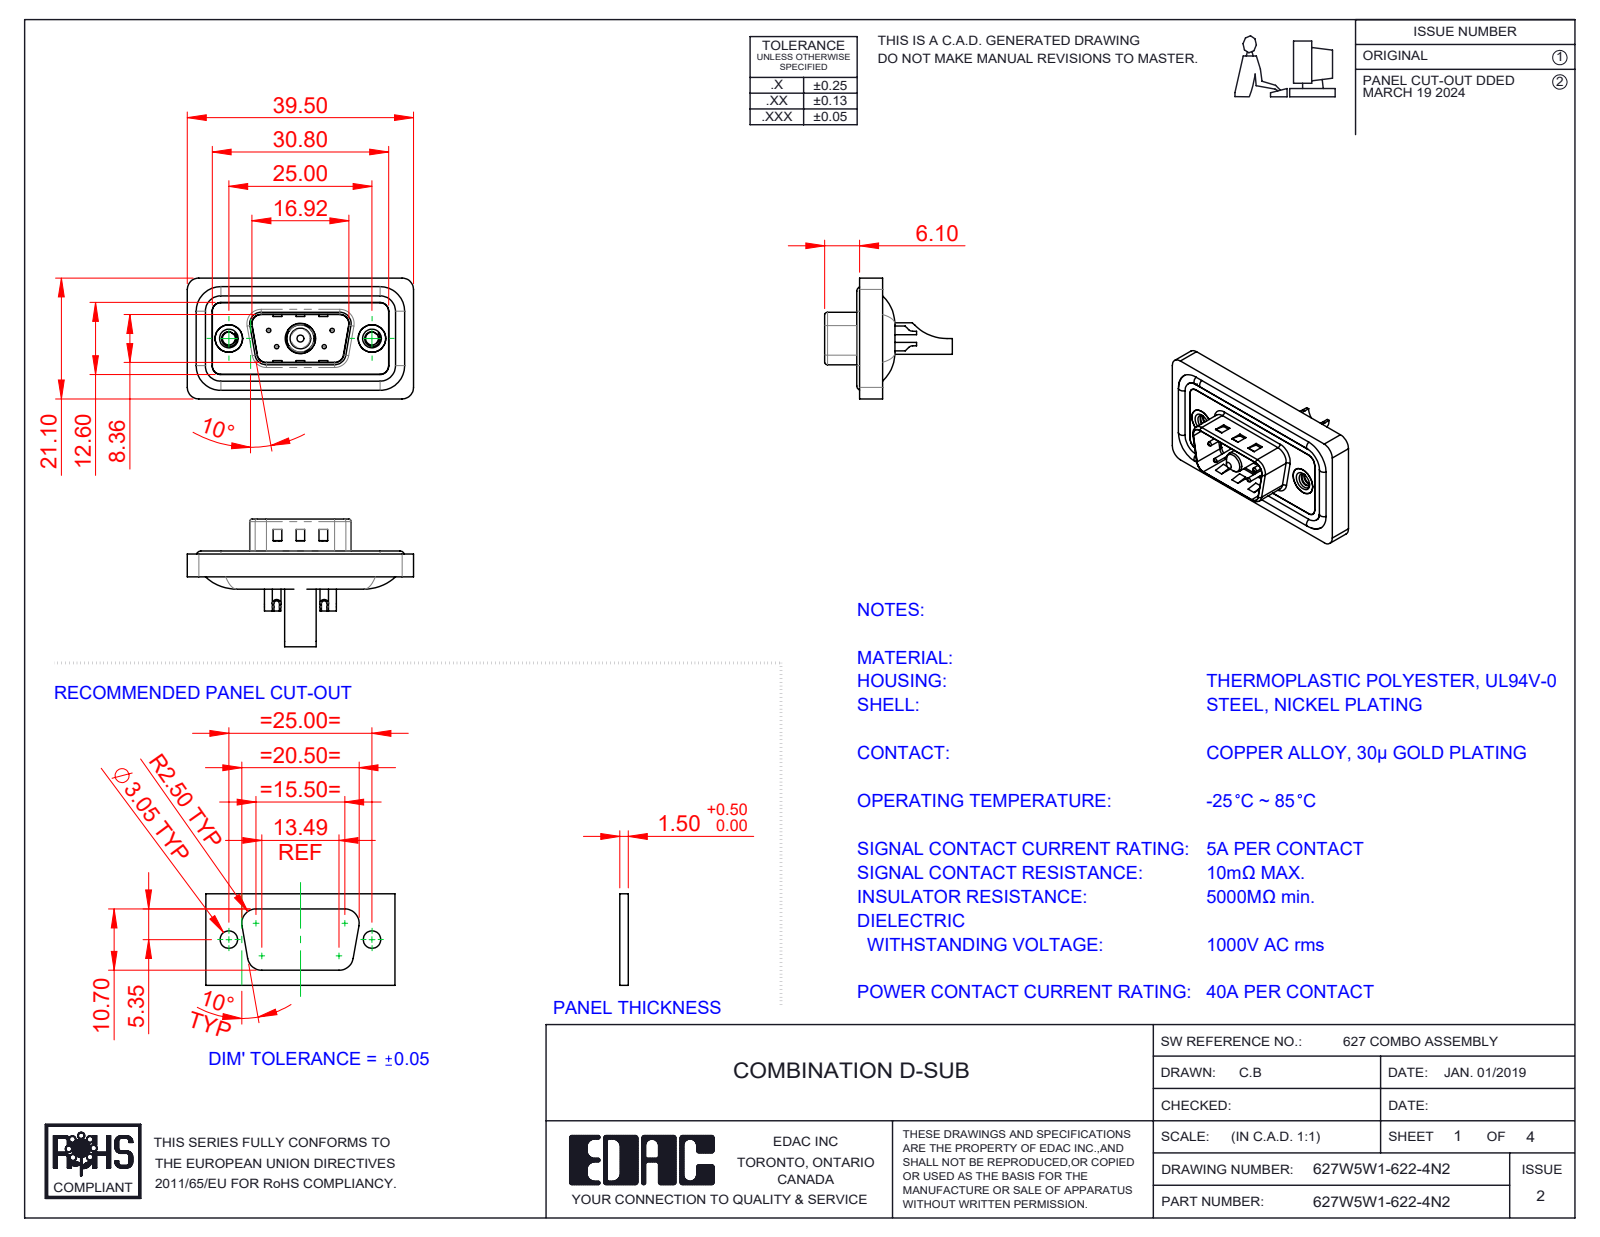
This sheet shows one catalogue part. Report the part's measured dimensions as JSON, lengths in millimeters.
{"part_name": "627Combo Waterproof Housing_09 Contacts; 627W5W1-622-4N2; 627Combo Threaded Rivet_2; 627Combo Contact Row 2_22 (+5 more)", "step_written_by": "SolidWorks 2023 (CONFIG_CONTROL_DESIGN)", "units": "millimeters", "bodies": {"solids": 13, "faces": 602, "planar": 193, "cylindrical": 264, "other": 145}, "overall_size": [39.5, 22.3, 21.1], "volume_mm3": 4434, "surface_area_mm2": 7113, "round_holes": [[0.75, 4], [1, 4], [1.6, 4], [2, 4], [2.26, 2], [4, 2], [4.8, 2], [5, 2], [4.6, 1], [4.85, 1], [5.3, 1]], "round_bosses_or_shafts": [[1.6, 4], [1.5, 4], [4.9, 2], [5.5, 1], [5.2, 1], [4.75, 1], [3.75, 1], [3.6, 1]], "partial_cylinders_radius": [[1.5, 22], [2, 18], [0.5, 8], [1.6, 8], [1, 6], [0.25, 4], [0.6, 4], [0.65, 4]], "face_to_face_distances": [0.4, 1.1, 2.9, 1.6, 3.1, 0.5, 1.5, 2.5, 4, 0.8], "hole_center_spacings": [3.16, 5.72, 7.1, 12.5, 18.1, 4.39, 4.4, 8.31]}
